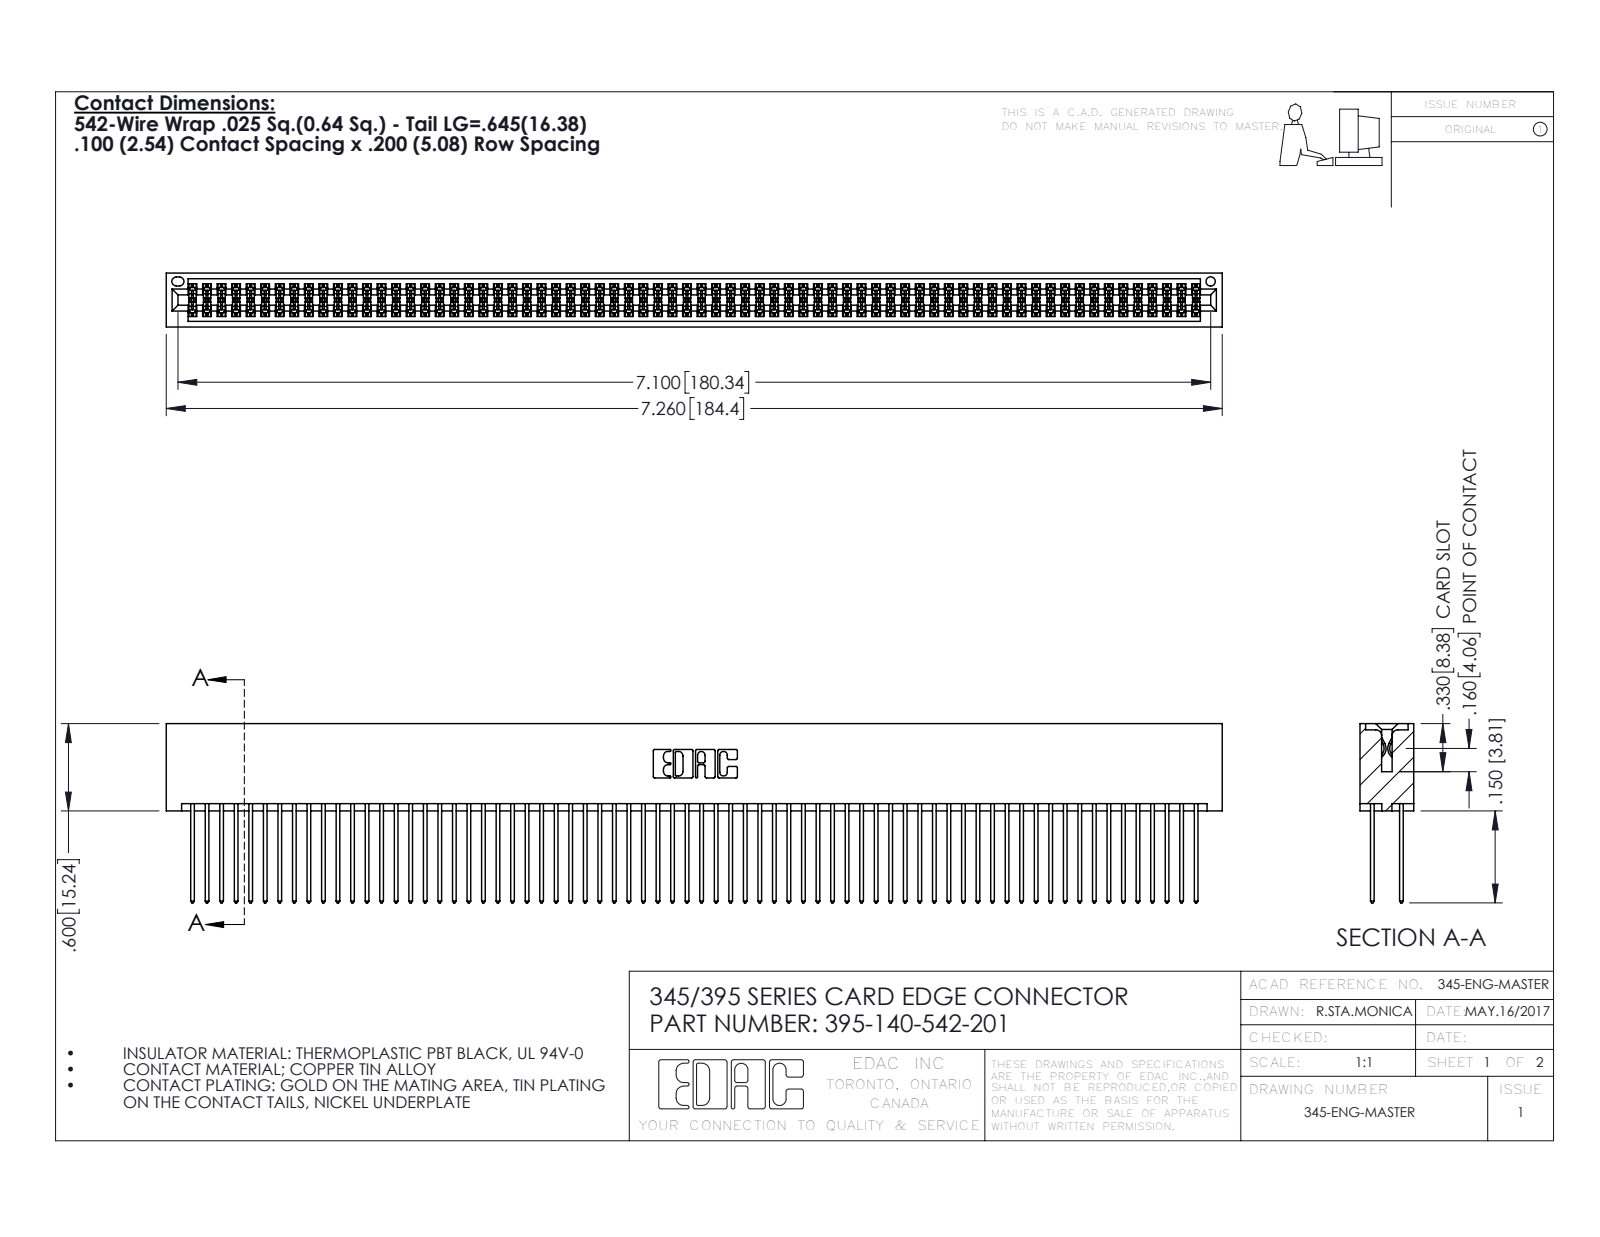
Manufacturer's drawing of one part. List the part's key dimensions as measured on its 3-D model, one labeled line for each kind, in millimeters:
Part name (STEP PRODUCT): 395-140-542-201; 345 Part_No Mounting Lugs; 345-292-001_345-293-142
STEP written by: SolidWorks 2016 (CONFIG_CONTROL_DESIGN)
Units: millimetres
Bodies: 141 solids, 7118 faces (4696 planar, 2422 cylindrical, 0 other)
Overall size (bounding box): 184.4 × 31.3 × 9.4
Volume: 19 440 mm³ · Surface area: 32 630 mm²
Round holes (diameter × count): ⌀1.6 ×1
Partial cylindrical surfaces — rounded edges, fillets, slot ends (radius × count): R0.2 ×210, R0.3 ×140, R0.3 ×22, R0.2 ×6, R0.8 ×6, R0.7 ×3, R0.4 ×2, R0.5 ×2
Main face-to-face distances: 7.6, 1.8, 5.1, 2.5, 6.9, 0.6, 5.7, 9.4, 4.4, 3.8
